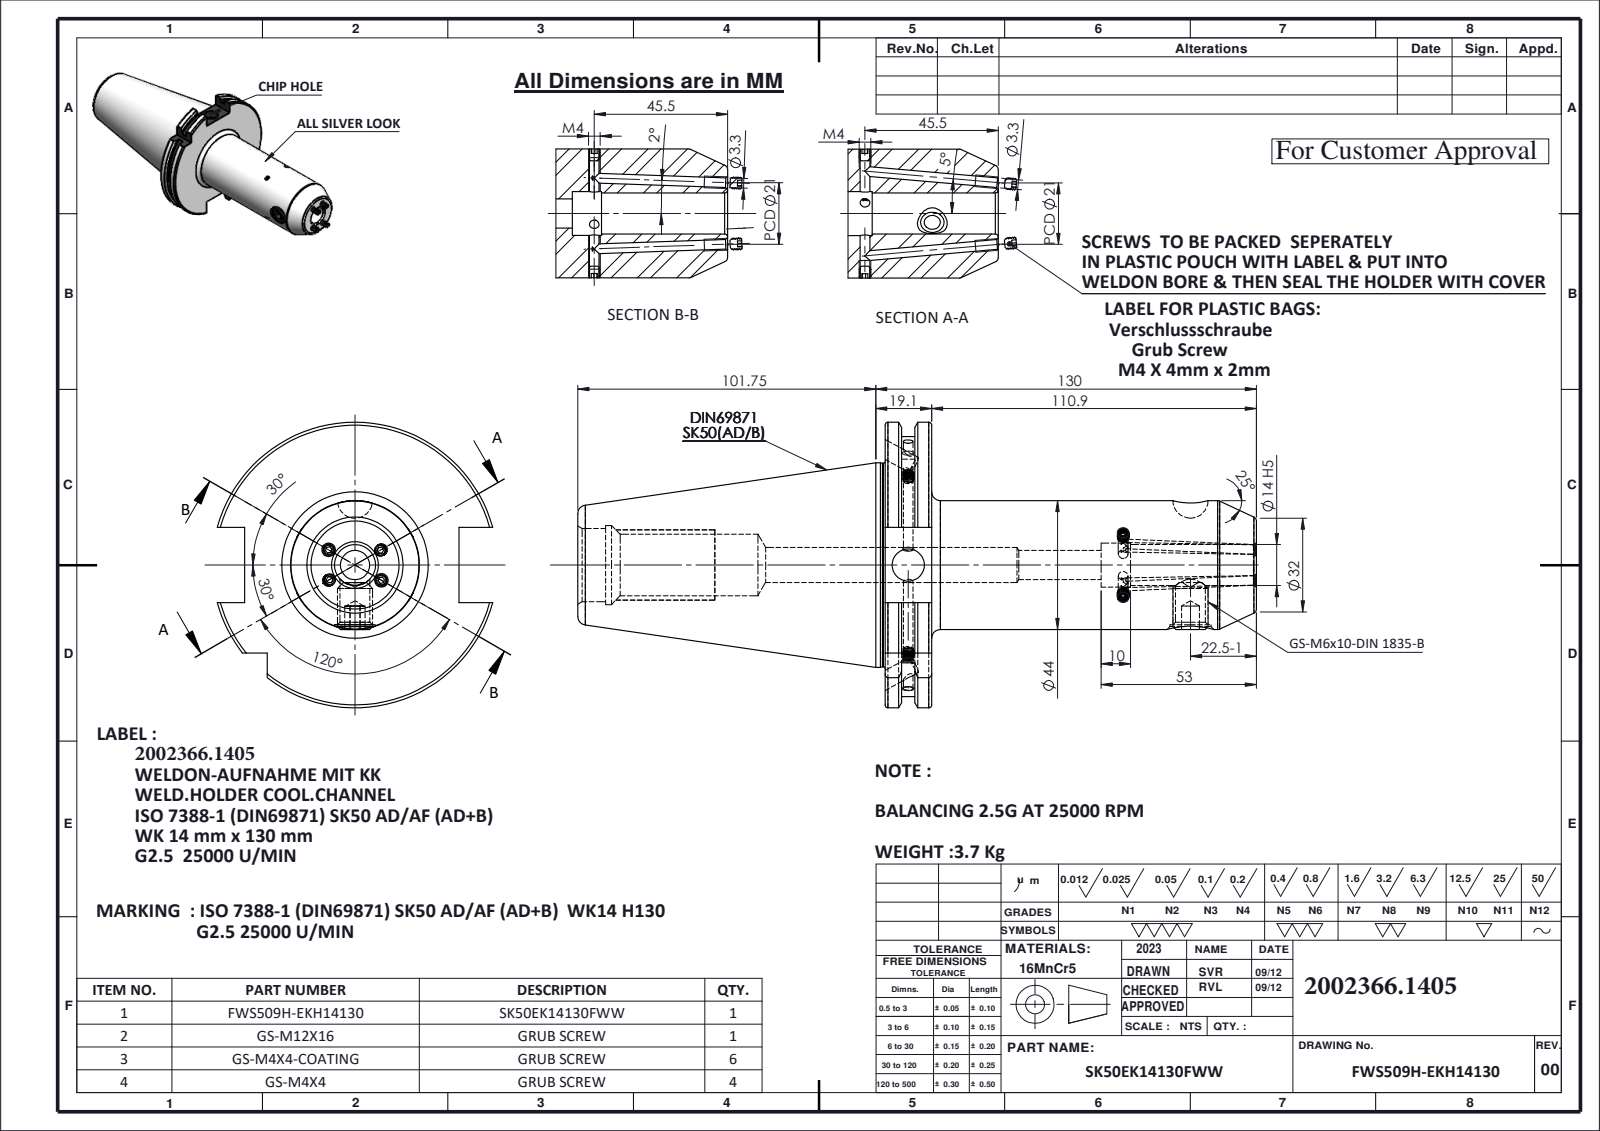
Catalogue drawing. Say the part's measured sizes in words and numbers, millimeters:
The part is named "SK50EK14130FWW; GS-M4X4-COATING_DIN 913 - M4 x 4-N; FWS509H-EKH14130; GS-M4X4_DIN 913 - M4 x 4-N (+1 more)". Its 3-D file was written by "SolidWorks 2023 (CONFIG_CONTROL_DESIGN)". It is 13 solids with 664 faces: 131 planar, 183 cylindrical and 350 other. Overall it measures 238.09 by 97.5 by 94.05 millimeters. Its volume is 479 177 cubic millimeters and its surface area 70 760 square millimeters. Round holes: 8 of diameter 3.3, 2 of diameter 6, 2 of diameter 14, 1 of diameter 10, 1 of diameter 10.2, 1 of diameter 11, 1 of diameter 12, 1 of diameter 15, 1 of diameter 21, 1 of diameter 25, 1 of diameter 27. Round bosses or shafts: 10 of diameter 4, 1 of diameter 69.85, 1 of diameter 69.45, 1 of diameter 44, 1 of diameter 12. Partial cylindrical surfaces (rounded edges, fillets, slot ends): 1 of radius 44.9, 1 of radius 48.75. The main face-to-face distances are 15.9, 5.65, 10.25, 10.14, 4.49, 5.76, 126.8, 121.15, 116.66, 110.9.
